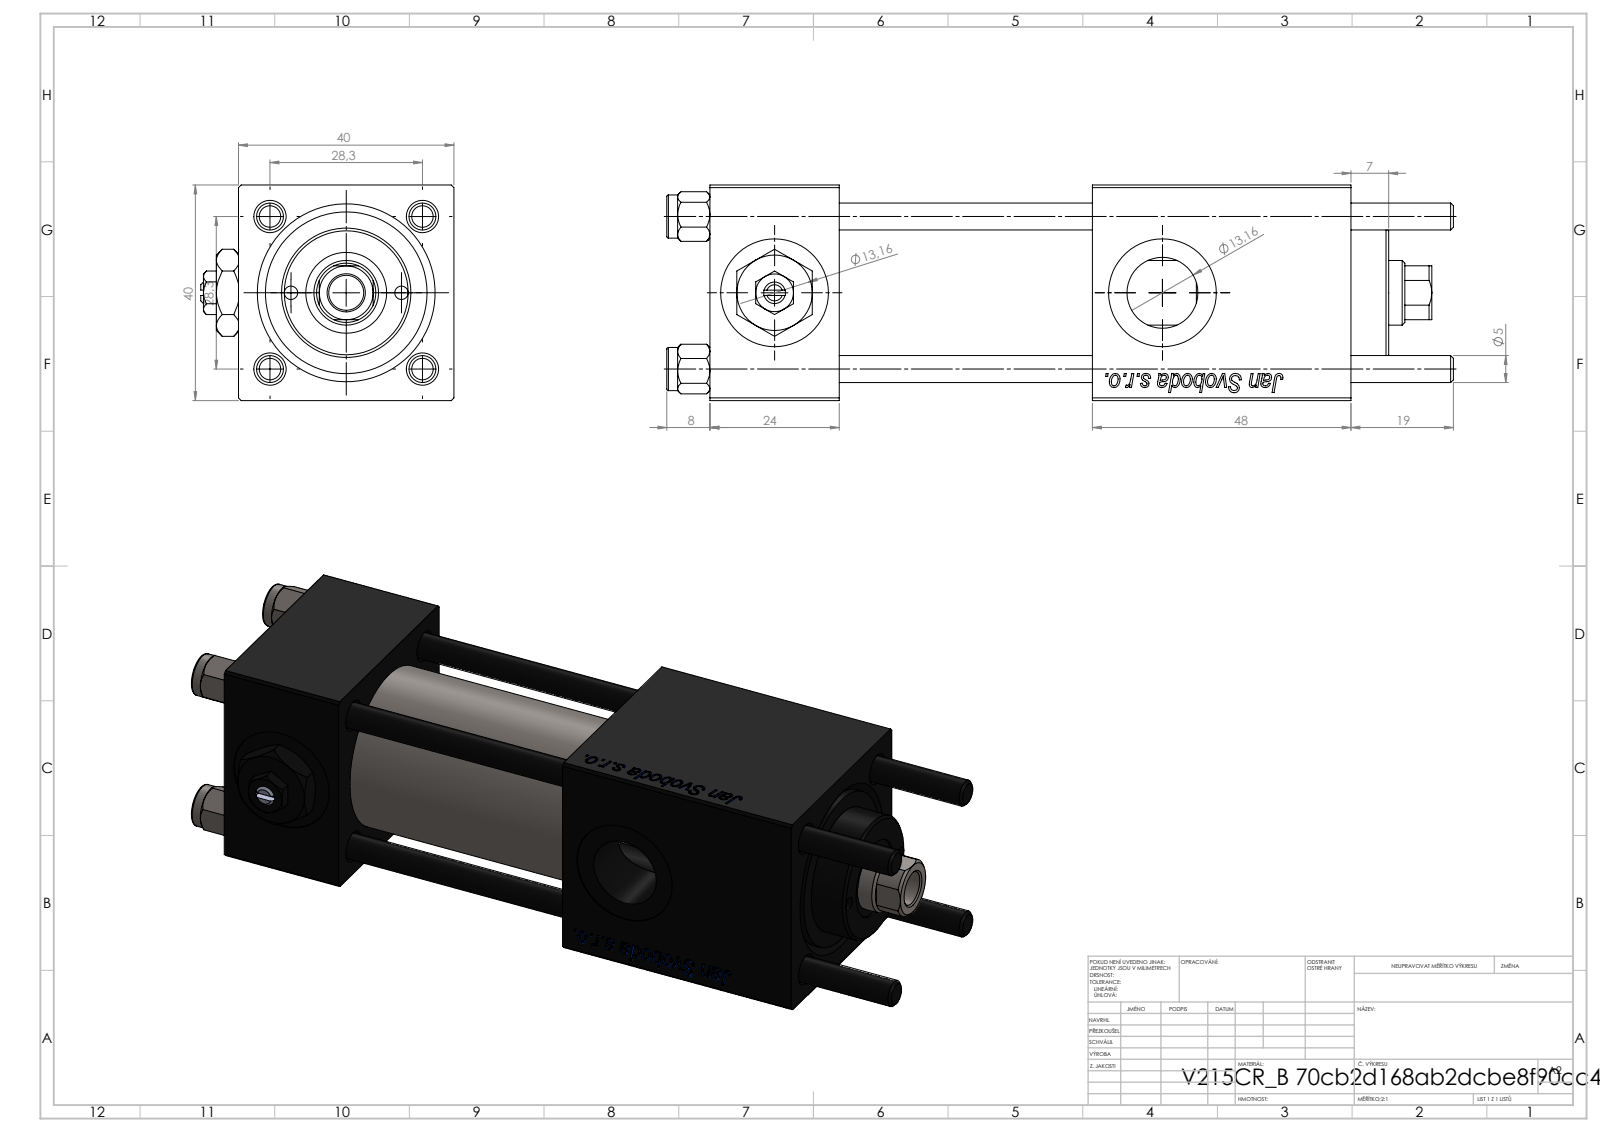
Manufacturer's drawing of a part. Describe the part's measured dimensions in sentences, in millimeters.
The part is named "NUT_M5_B; V215CR_B_TYCINKA; V215_VC_A; V215CR_B-1 (+2 more)". Its 3-D file was written by "SolidWorks 2019 (CONFIG_CONTROL_DESIGN)". It is 12 solids with 1214 faces: 454 planar, 90 cylindrical and 670 other. Overall it measures 146 by 47 by 40 millimeters. Its volume is 144 013 cubic millimeters and its surface area 59 832 square millimeters. Round holes: 4 of diameter 5, 3 of diameter 20, 2 of diameter 2.5, 2 of diameter 7, 2 of diameter 13.16, 1 of diameter 6.5, 1 of diameter 12, 1 of diameter 15, 1 of diameter 25, 1 of diameter 30. Round bosses or shafts: 4 of diameter 8, 1 of diameter 31, 1 of diameter 24. Partial cylindrical surfaces (rounded edges, fillets, slot ends): 1 of radius 5.5. The main face-to-face distances are 40, 24, 90.3, 66.3, 119, 47, 71, 19.3, 95, 48. The hole center spacings are 14.68, 20.01, 28.21, 28.3, 10.25, 40.02, 20.5, 72.
